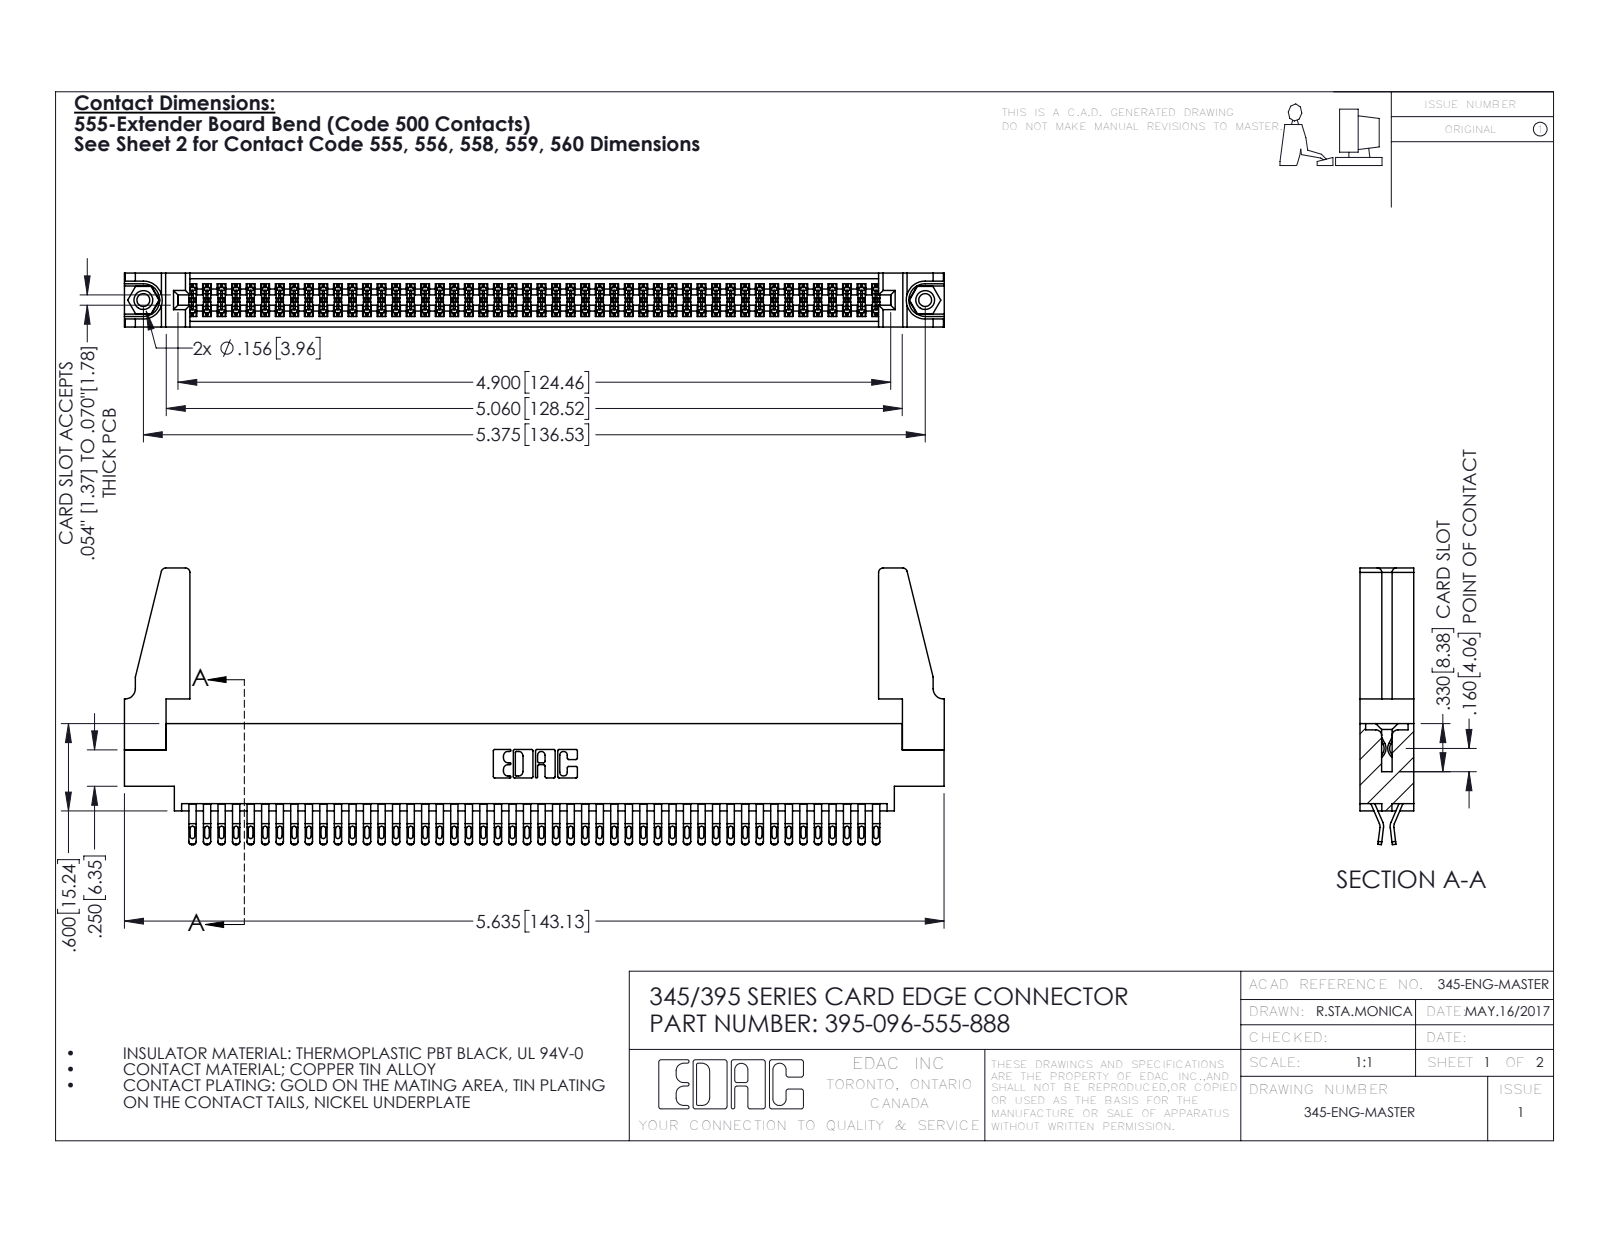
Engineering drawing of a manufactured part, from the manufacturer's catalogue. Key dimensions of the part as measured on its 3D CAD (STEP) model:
Part name (STEP PRODUCT): 345-250-001_345-250-001-102; 345 Part_0.170 Offset - 0.156 Dia-TH; 395-096-555-888; 345-220-078_345-220-088 (+1 more)
STEP written by: SolidWorks 2016 (CONFIG_CONTROL_DESIGN)
Units: inches
Bodies: 101 solids, 5630 faces (3132 planar, 2482 cylindrical, 16 other)
Overall size (bounding box): 5.636 × 1.902 × 0.37
Volume: 1.061 in³ · Surface area: 39.11 in²
Round holes (diameter × count): ⌀0.089 ×2, ⌀0.125 ×2, ⌀0.156 ×2, ⌀0.064 ×1
Round bosses / shafts (diameter × count): ⌀0.155 ×2
Partial cylindrical surfaces — rounded edges, fillets, slot ends (radius × count): R0.016 ×240, R0.02 ×192, R0.006 ×144, R0.01 ×22, R0.03 ×8, R0.007 ×6, R0.031 ×6, R0.026 ×3
Main face-to-face distances: 0.072, 0.298, 0.37, 0.025, 0.098, 0.272, 0.2, 0.225, 0.175, 0.149
Hole centre spacings: 0.27, 5.139, 5.375
